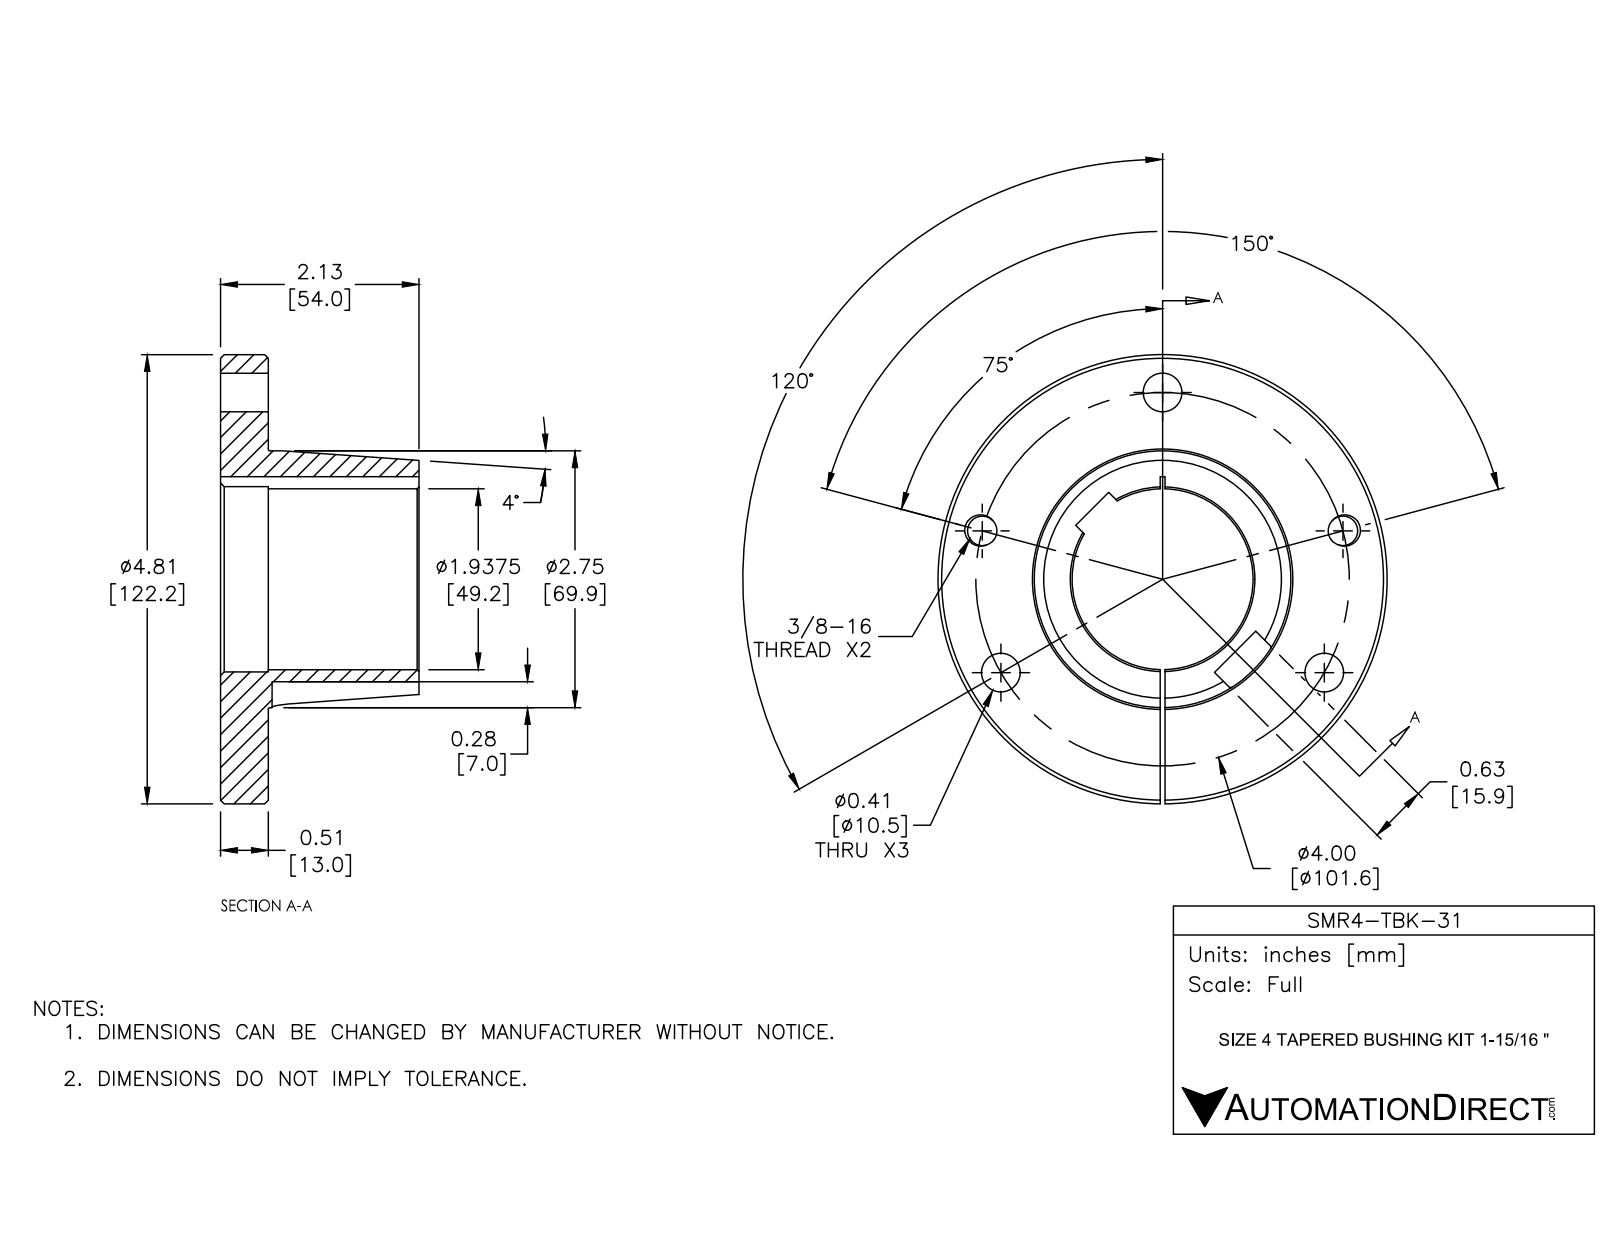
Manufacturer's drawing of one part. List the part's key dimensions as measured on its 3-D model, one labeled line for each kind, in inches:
Part name (STEP PRODUCT): SMR4-TBK-31
STEP written by: SolidWorks 2016 (AUTOMOTIVE_DESIGN)
Units: inches
Bodies: 1 solid, 137 faces (18 planar, 96 cylindrical, 23 other)
Overall size (bounding box): 4.811 × 4.811 × 2.126
Volume: 11.2 in³ · Surface area: 69.23 in²
Round holes (diameter × count): ⌀0.413 ×3, ⌀0.315 ×2, ⌀0.375 ×2, ⌀1.937 ×1, ⌀1.985 ×1
Round bosses / shafts (diameter × count): ⌀4.811 ×1, ⌀2.75 ×1
Partial cylindrical surfaces — rounded edges, fillets, slot ends (radius × count): R0.197 ×2
Main face-to-face distances: 0.512, 2.126, 1.614, 0.051, 2.165, 0.063, 0.563, 0.5, 0.625, 0.551
Hole centre spacings: 2, 1.531, 2.435, 3.464, 3.966, 3.464, 3.864
